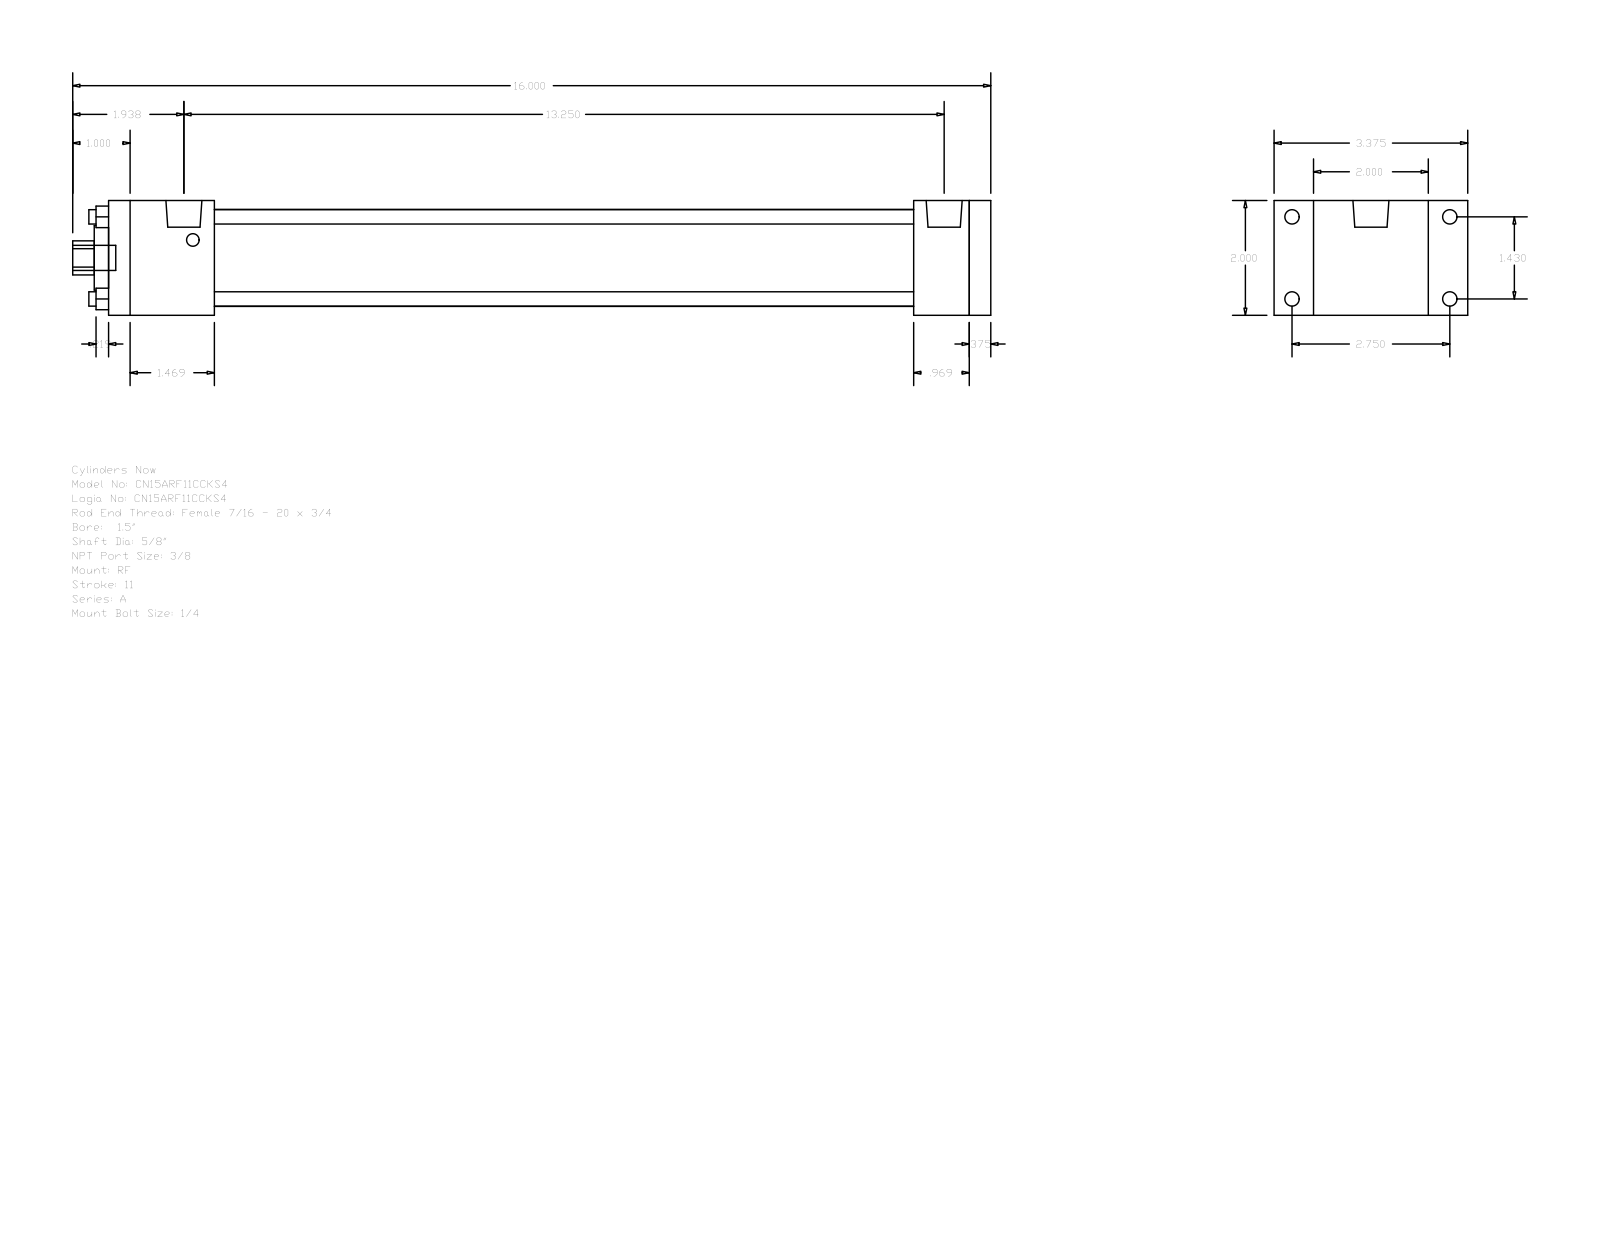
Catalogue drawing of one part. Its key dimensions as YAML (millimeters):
part_name: "A_RF__0150_0.625"
step_written_by: "GSSL Pune (CONFIG_CONTROL_DESIGN)"
units: millimeters
bodies: {solids: 0, faces: 92, planar: 64, cylindrical: 28, other: 0}
overall_size: [406.4, 85.72, 50.8]
round_holes:
  - {diameter: 6.35, count: 4}
  - {diameter: 15.88, count: 1}
  - {diameter: 28.57, count: 1}
  - {diameter: 42.93, count: 1}
round_bosses_or_shafts:
  - {diameter: 6.35, count: 4}
  - {diameter: 5.56, count: 4}
  - {diameter: 15.93, count: 2}
  - {diameter: 11.11, count: 1}
partial_cylinders:
  - {radius: 7.54, count: 1}
face_to_face_distances: [50.8, 9.52, 381, 390.52, 356.39, 24.61, 34.13, 46.83, 309.56, 334.17]
hole_center_spacings: [25.68, 36.32, 51.36]
